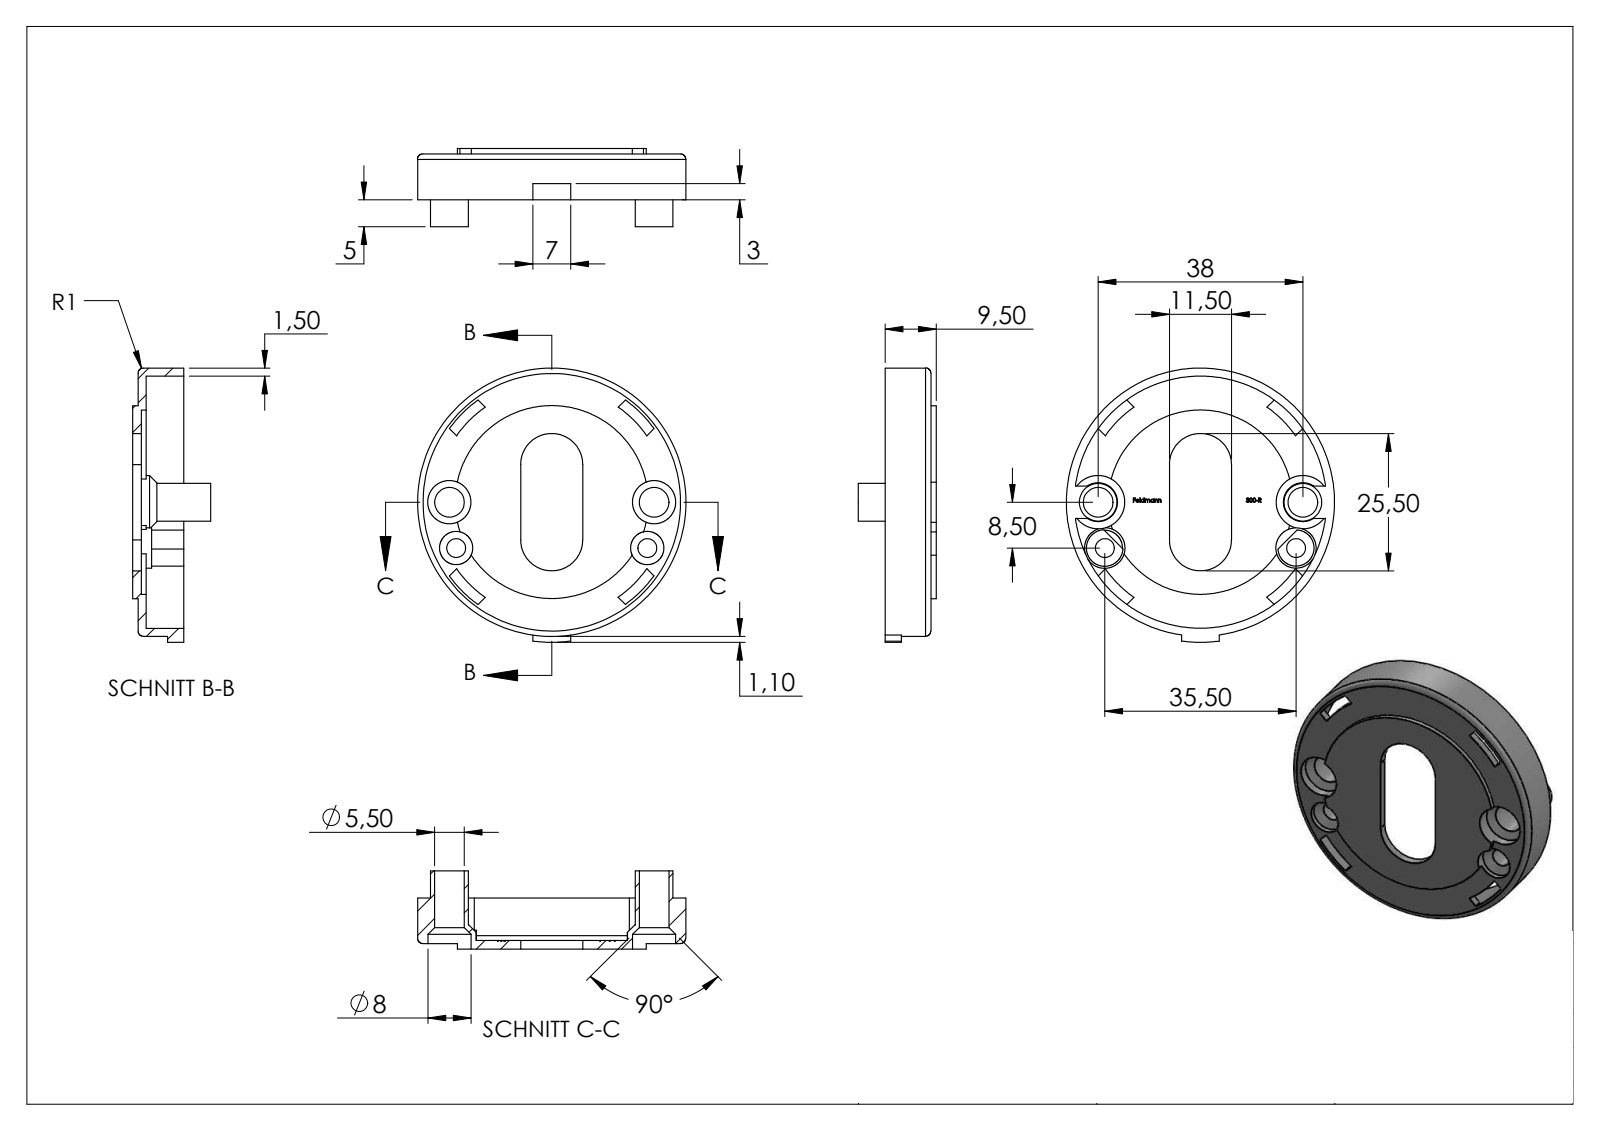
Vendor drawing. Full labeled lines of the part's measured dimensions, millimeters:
Part name (STEP PRODUCT): 30X-R Teil1_300-R Teil1; 30X-R Teil2_300-R Teil2; 30X-R Teil1; 300-R (+1 more)
STEP written by: SolidWorks 2015 (CONFIG_CONTROL_DESIGN)
Units: millimetres
Bodies: 2 solids, 276 faces (136 planar, 45 cylindrical, 95 other)
Overall size (bounding box): 52 × 52 × 15.5
Volume: 8 082 mm³ · Surface area: 14 090 mm²
Round holes (diameter × count): ⌀3.5 ×2, ⌀5.5 ×2, ⌀6.2 ×2, ⌀8 ×2, ⌀46.8 ×1, ⌀50 ×1
Round bosses / shafts (diameter × count): ⌀7.5 ×2, ⌀7 ×2, ⌀52 ×1, ⌀49.8 ×1
Partial cylindrical surfaces — rounded edges, fillets, slot ends (radius × count): R0.5 ×2, R1 ×2, R3.35 ×2, R4.95 ×2, R5.75 ×2, R4.1 ×1, R4.25 ×1, R17.1 ×1
Main face-to-face distances: 1, 2, 0.6, 1.6, 2.6, 3.5, 1.5, 2.5, 0.9, 8.5
Hole centre spacings: 8.59, 19, 19.68, 37.72, 35.5, 38
